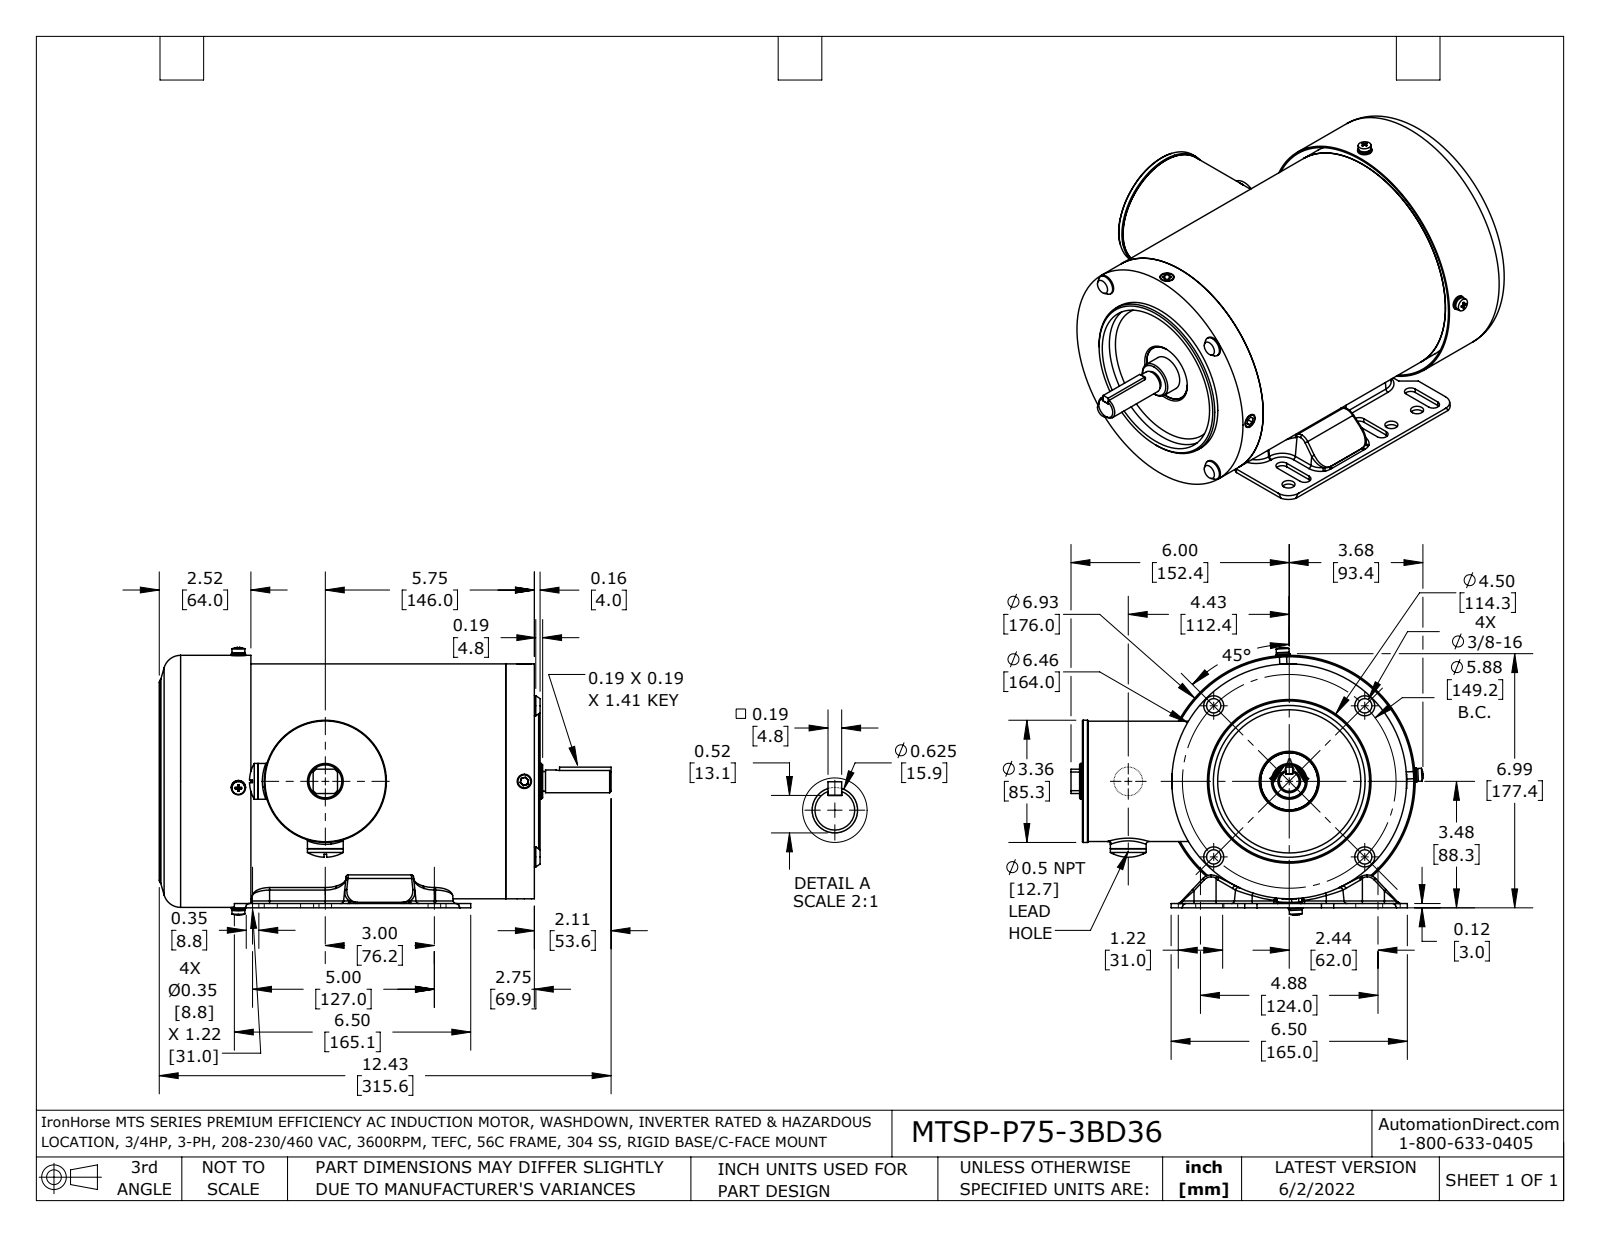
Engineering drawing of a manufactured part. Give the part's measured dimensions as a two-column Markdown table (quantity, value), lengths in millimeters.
| quantity | value |
| --- | --- |
| part name | MTSP-P75-3BD36 |
| STEP written by | SolidWorks 2021 (AUTOMOTIVE_DESIGN) |
| units | millimeters |
| bodies | 40 solids, 1658 faces (444 planar, 582 cylindrical, 632 other) |
| overall size | 315.6 × 245.9 × 186.9 |
| volume | 953 400 mm³ |
| surface area | 643 000 mm² |
| round holes (diameter × count) | 4.2 × 10, 5.5 × 8, 9.1 × 6, 5.4 × 4, 6 × 4, 6.5 × 4, 8.5 × 4, 3 × 2, 9 × 2, 12 × 2, 16.7 × 2, 35 × 2 |
| round bosses / shafts (diameter × count) | 10 × 6, 14 × 4, 9 × 4, 8.4 × 4, 8 × 4, 5 × 4, 25 × 3, 20 × 2 |
| partial cylindrical surfaces (radius × count) | 2 × 56, 1 × 39, 3.3 × 36, 0.3 × 16, 3 × 14, 4.4 × 12, 6 × 8, 1.5 × 6 |
| main face-to-face distances | 3, 211, 6, 1, 205, 208, 214, 49.5, 46.5, 260.5 |
| hole center spacings | 74.6, 105.5, 3.6, 30, 33.6, 56.7, 58.7, 63.4 |
